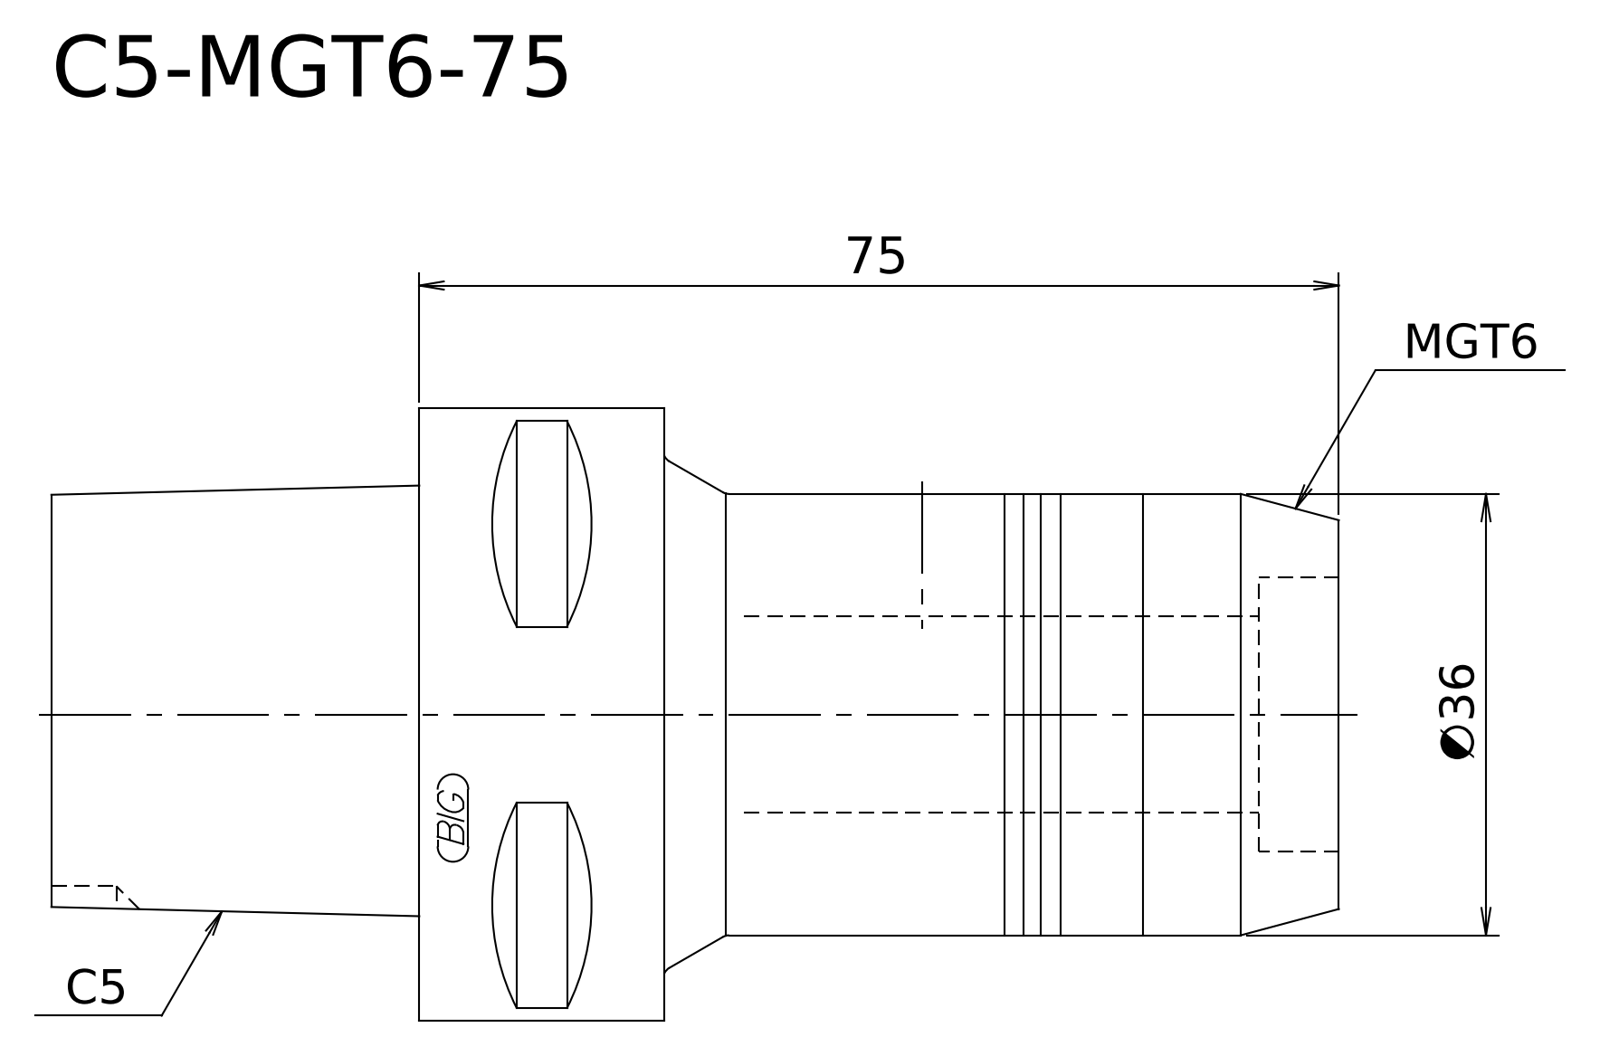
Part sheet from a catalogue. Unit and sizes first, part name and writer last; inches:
Units: inches
Overall size (bounding box): 4.134 × 1.968 × 1.968
Round bosses / shafts (diameter × count): ⌀1.968 ×1, ⌀1.417 ×1
Main face-to-face distances: 1.181, 2.953, 4.134, 2.165, 0.787, 1.969
Volume: 7.466 in³ · Surface area: 24.77 in²
Bodies: 1 solid, 9 faces (4 planar, 2 cylindrical, 3 other)
STEP written by: Kubotek KeyCreator V8.5.1 (14335) (CONFIG_CONTROL_DESIGN)
